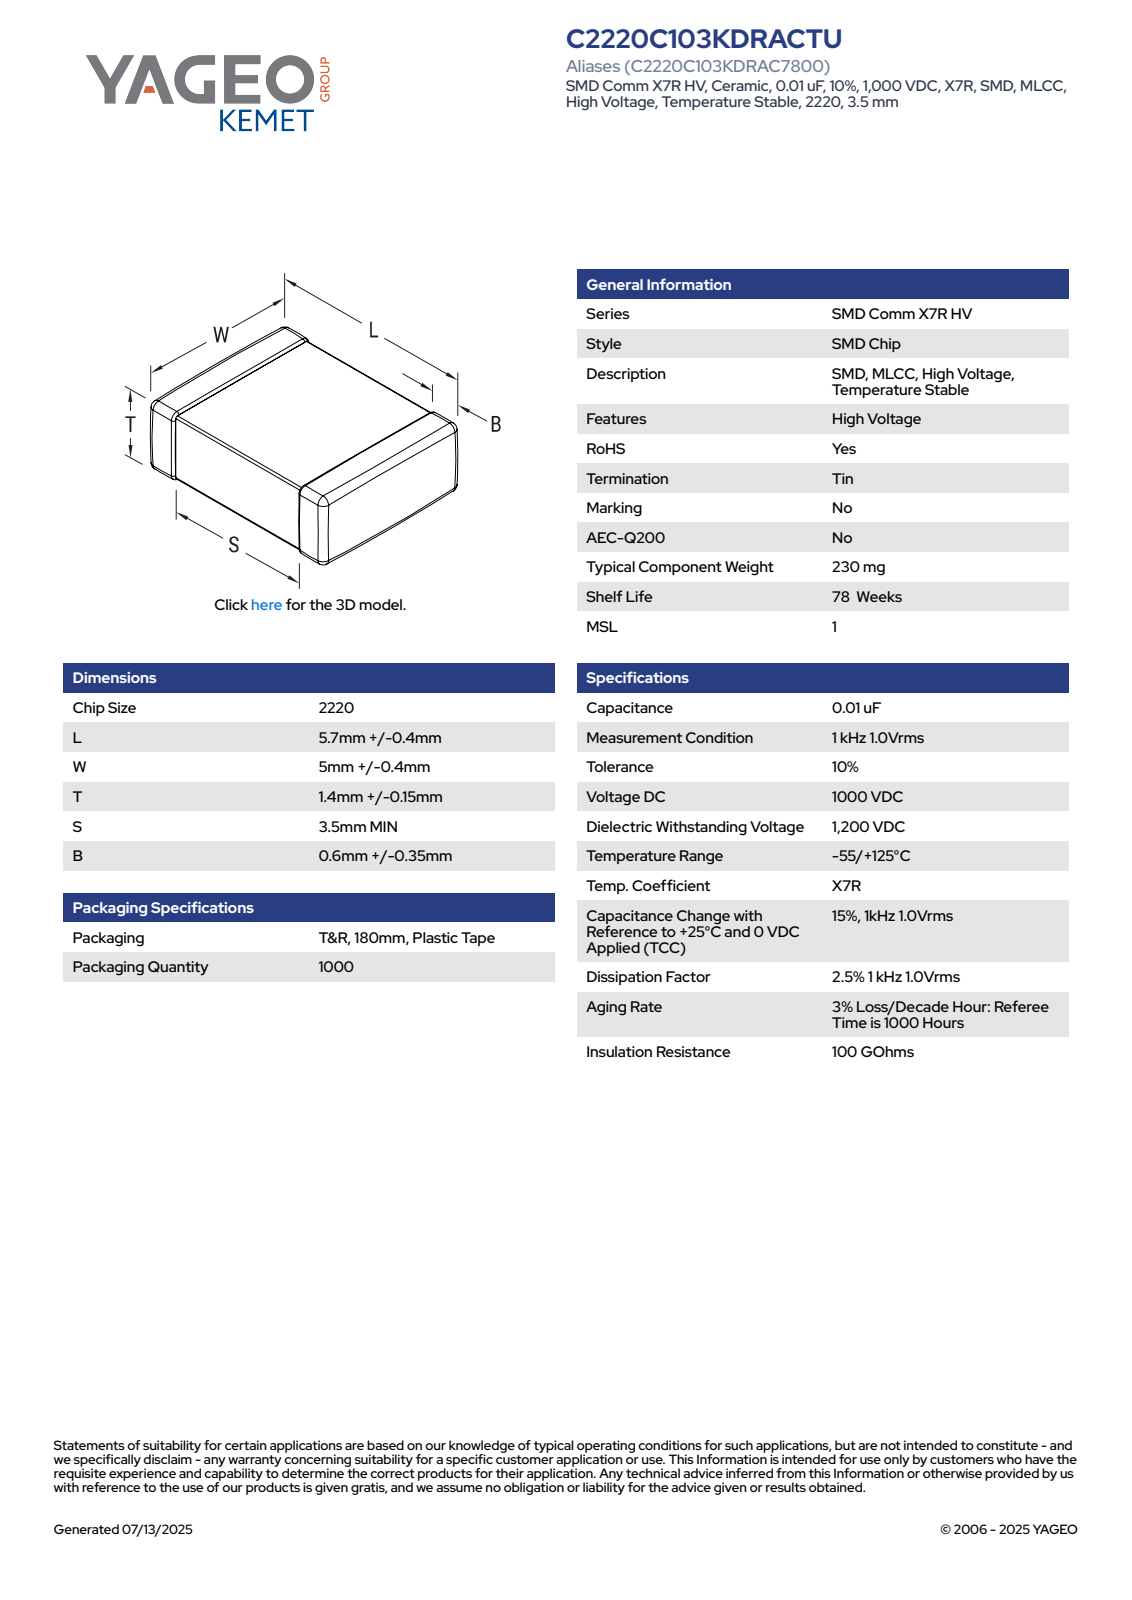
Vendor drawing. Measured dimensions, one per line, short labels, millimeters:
name: CCS_CCSTDNOS_2220_L6.1W5.4T1.55B0.95
written by: SolidWorks 2014 (AUTOMOTIVE_DESIGN)
unit: mm
bodies: 4 solids, 125 faces (71 planar, 38 cylindrical, 16 other)
size: 6.1 × 5.4 × 1.55
volume: 45 mm³; area: 98 mm²
rounds: 24× R0.11
face distances: 1.33, 1.44, 1.55, 6.1, 5.18, 5.29, 5.4, 2.66, 2.74, 2.55
